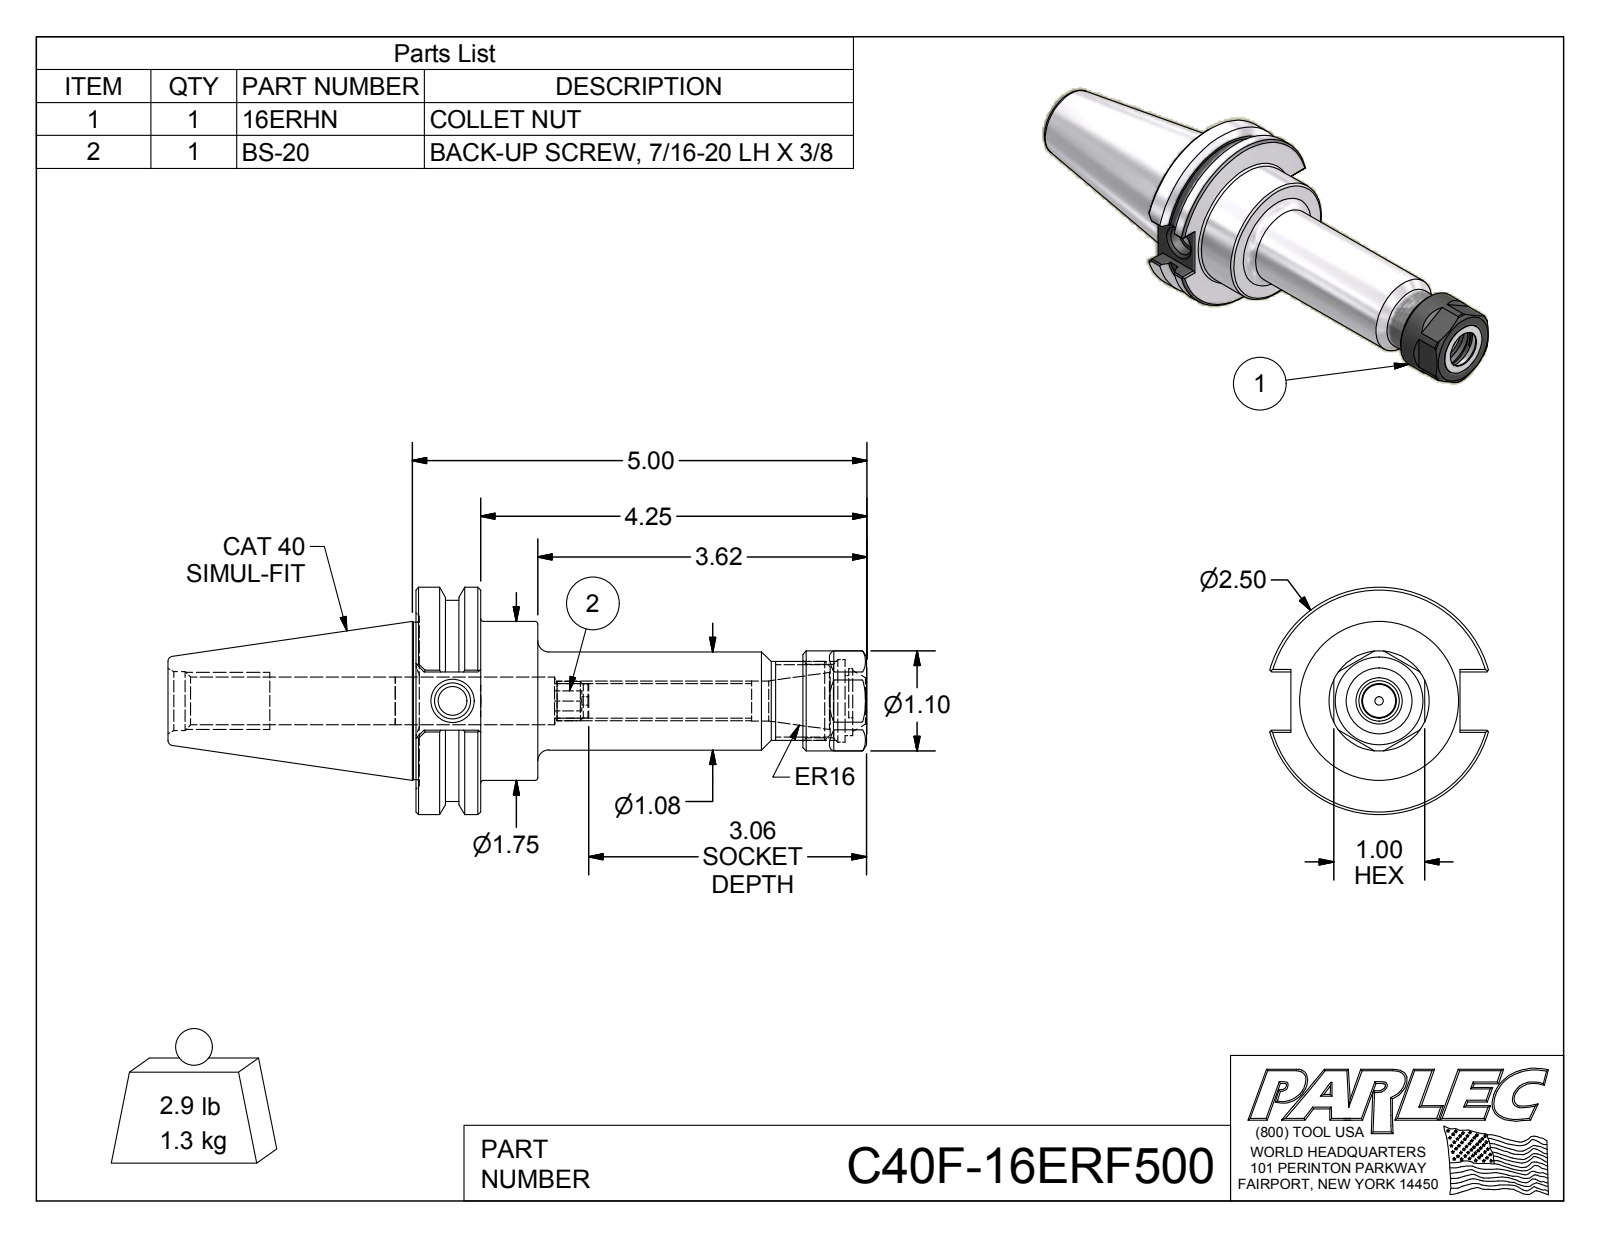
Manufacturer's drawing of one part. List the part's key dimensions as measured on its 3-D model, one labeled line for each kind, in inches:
Part name (STEP PRODUCT): C40F-16ER5-1; 16ERHN; BS-20; C40F-16ERF500
STEP written by: Autodesk Inventor 2016 (AUTOMOTIVE_DESIGN)
Units: inches
Bodies: 3 solids, 129 faces (59 planar, 26 cylindrical, 44 other)
Overall size (bounding box): 7.687 × 2.5 × 2.406
Volume: 10.25 in³ · Surface area: 56.84 in²
Round holes (diameter × count): ⌀0.09 ×1, ⌀0.315 ×1, ⌀0.383 ×1, ⌀0.399 ×1, ⌀0.44 ×1, ⌀0.488 ×1, ⌀0.527 ×1, ⌀0.527 ×1, ⌀0.648 ×1, ⌀0.67 ×1, ⌀0.807 ×1, ⌀0.906 ×1
Round bosses / shafts (diameter × count): ⌀2.5 ×1, ⌀2.215 ×1, ⌀1.75 ×1, ⌀1.102 ×1, ⌀1.08 ×1, ⌀0.866 ×1, ⌀0.432 ×1, ⌀0.372 ×1
Partial cylindrical surfaces — rounded edges, fillets, slot ends (radius × count): R0.285 ×1, R0.354 ×1
Main face-to-face distances: 0.71, 1.34, 0.63, 4.96, 4.25, 3.62, 0.99, 4.736, 4.026, 3.396
Hole centre spacings: 0.06
